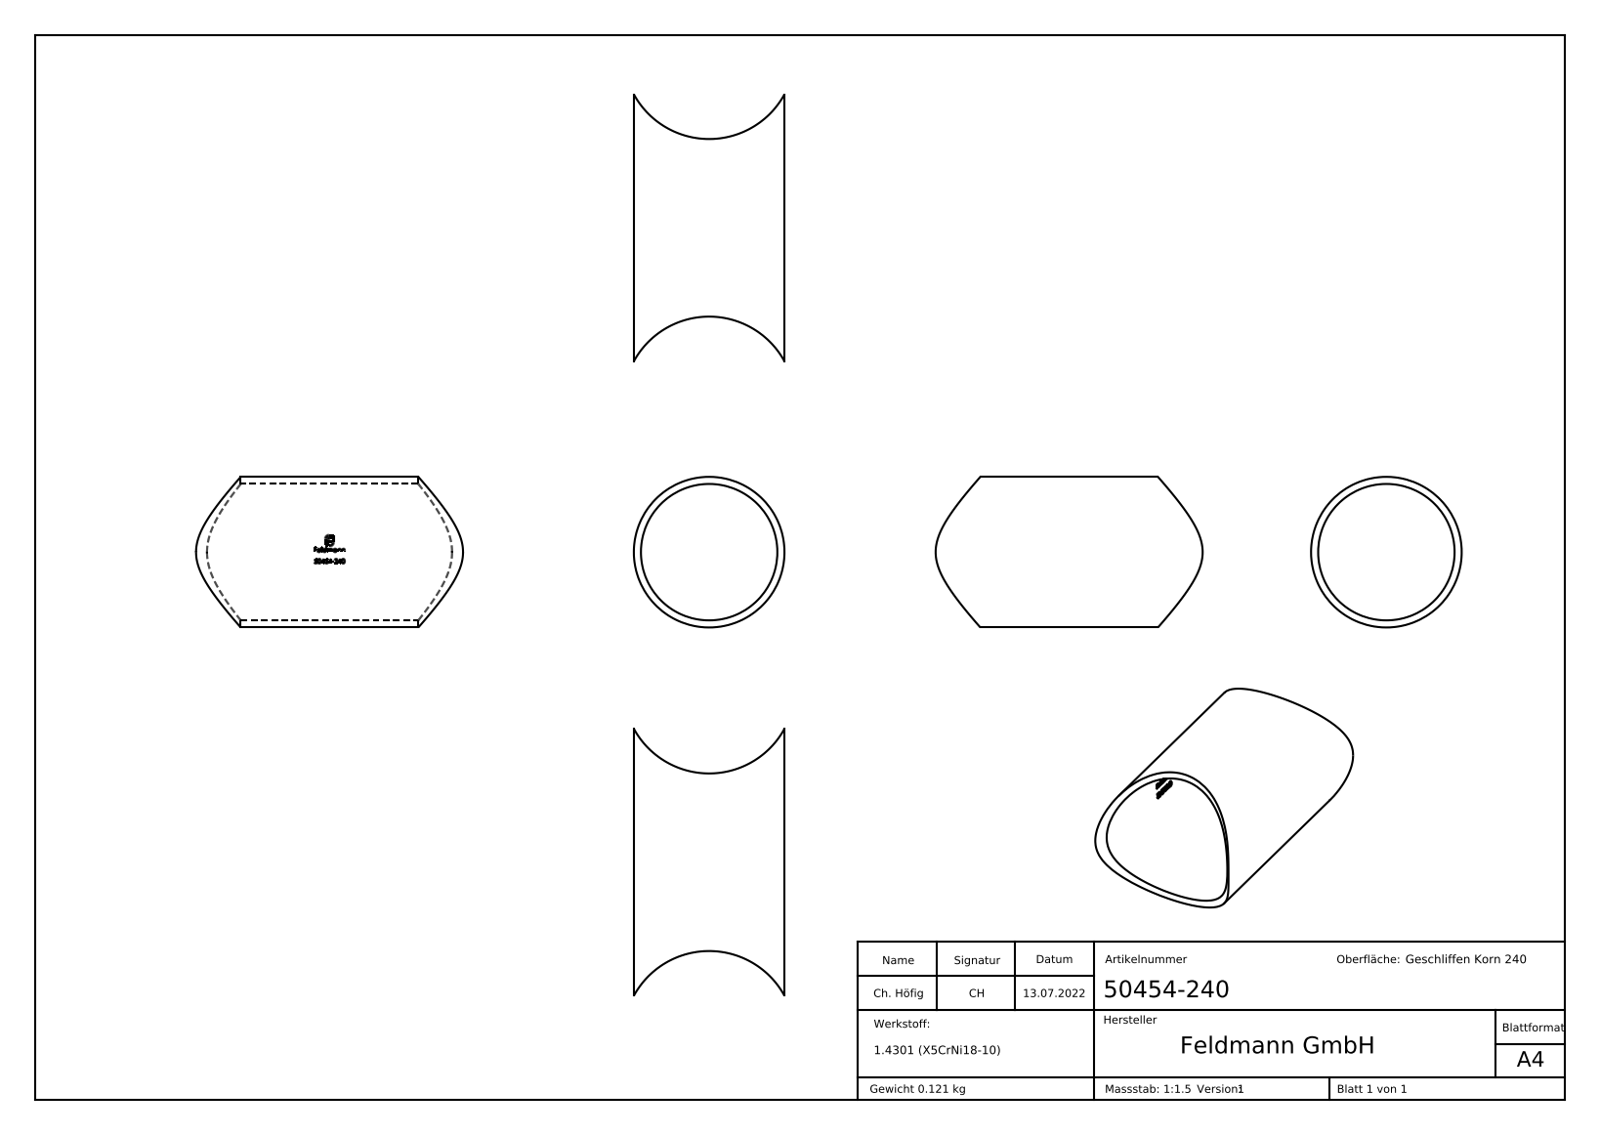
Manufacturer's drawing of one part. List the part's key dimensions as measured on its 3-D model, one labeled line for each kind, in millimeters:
Part name (STEP PRODUCT): 50454-240
STEP written by: SolidWorks 2018 (CONFIG_CONTROL_DESIGN)
Units: millimetres
Bodies: 1 solid, 275 faces (137 planar, 30 cylindrical, 108 other)
Overall size (bounding box): 75.17 × 42.4 × 42.4
Volume: 15 277 mm³ · Surface area: 15 982 mm²
Round holes (diameter × count): ⌀38.4 ×1
Round bosses / shafts (diameter × count): ⌀42.4 ×1
Partial cylindrical surfaces — rounded edges, fillets, slot ends (radius × count): R24.15 ×2, R19.3 ×1
Main face-to-face distances: 4.39, 0.58, 1.82, 2.9, 0.88, 2.52, 3.27, 0.92, 2.65, 0.34
